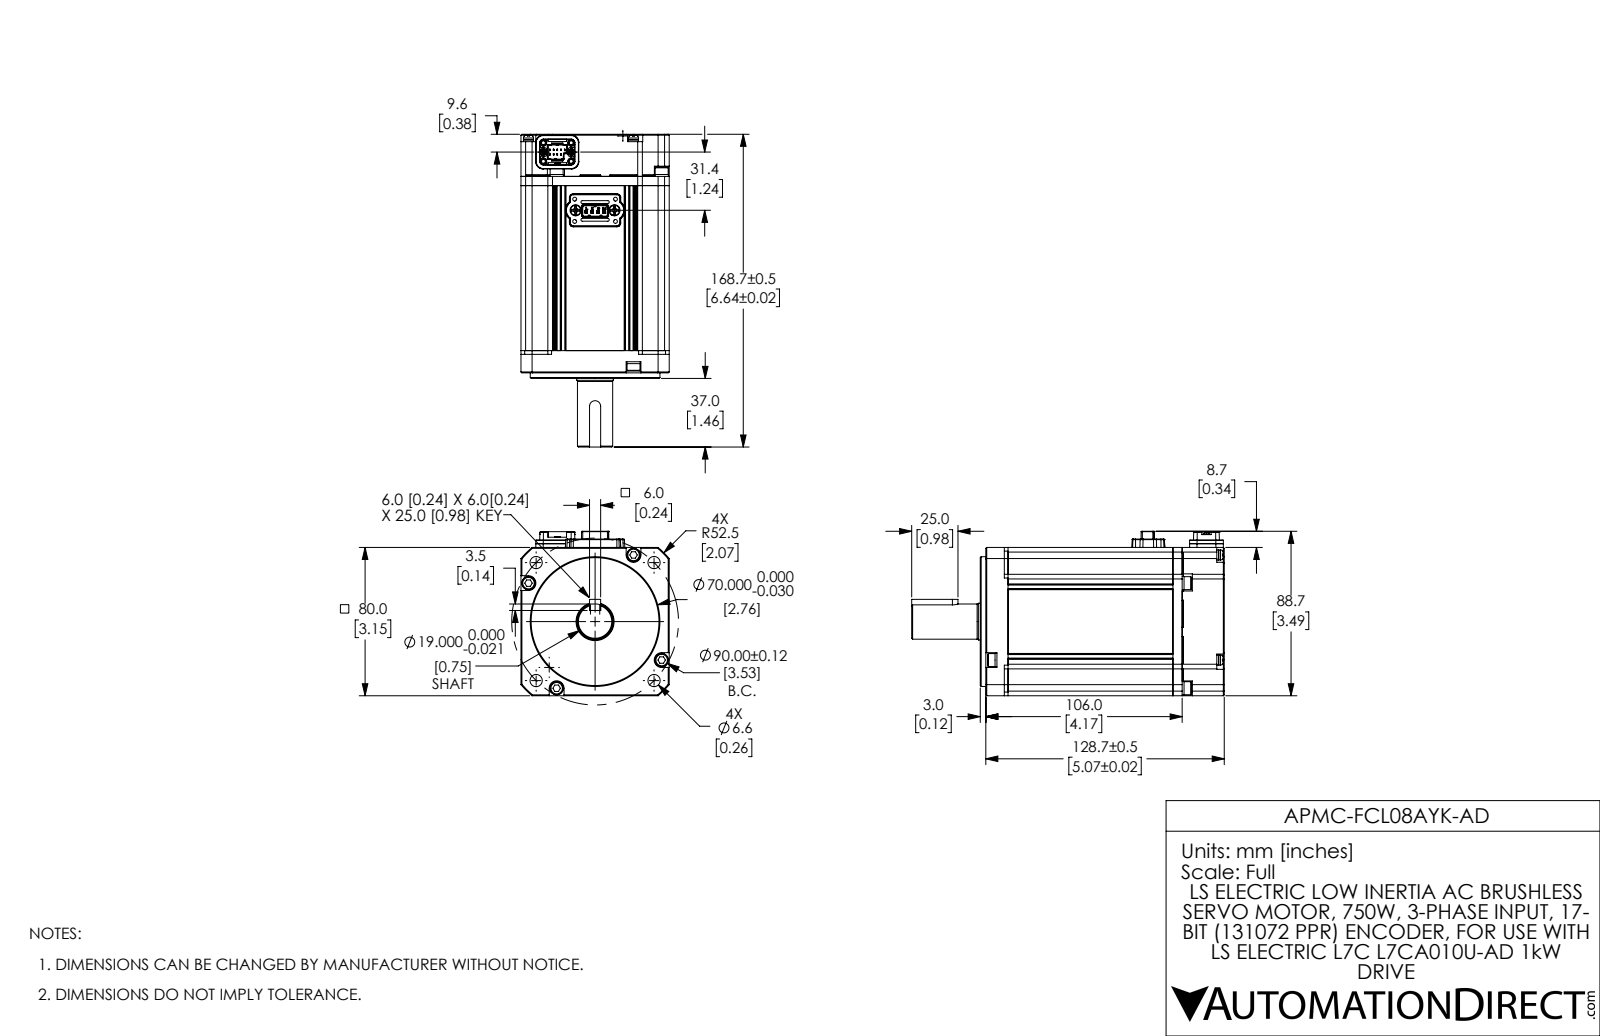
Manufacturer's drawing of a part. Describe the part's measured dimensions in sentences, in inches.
The part is named "APMC-FCL08AYK-AD". Its 3-D file was written by "SolidWorks 2017 (AUTOMOTIVE_DESIGN)". It is 45 solids with 1874 faces: 1220 planar, 474 cylindrical and 180 other. Overall it measures 6.642 by 3.492 by 3.15 inches. Its volume is 45.55 cubic inches and its surface area 182.9 square inches. Round holes: 10 of diameter 0.083, 8 of diameter 0.157, 8 of diameter 0.177, 6 of diameter 0.118, 4 of diameter 0.138, 4 of diameter 0.26, 2 of diameter 0.079, 2 of diameter 0.236, 1 of diameter 0.13, 1 of diameter 0.134, 1 of diameter 0.807. Round bosses or shafts: 8 of diameter 0.283, 8 of diameter 0.276, 6 of diameter 0.213, 2 of diameter 0.087, 1 of diameter 2.756, 1 of diameter 0.78, 1 of diameter 0.748. Partial cylindrical surfaces (rounded edges, fillets, slot ends): 36 of radius 0.012, 20 of radius 0.008, 9 of radius 0.006, 9 of radius 0.098, 9 of radius 0.157, 8 of radius 0.039, 8 of radius 0.079, 7 of radius 0.018. The main face-to-face distances are 0.197, 3.504, 3.701, 3.15, 0.028, 0.224, 3.728, 0.866, 4.594, 0.894. The hole center spacings are 1.634, 0.465, 2.076, 2.311, 2.703, 3.376, 0.197, 0.237.
